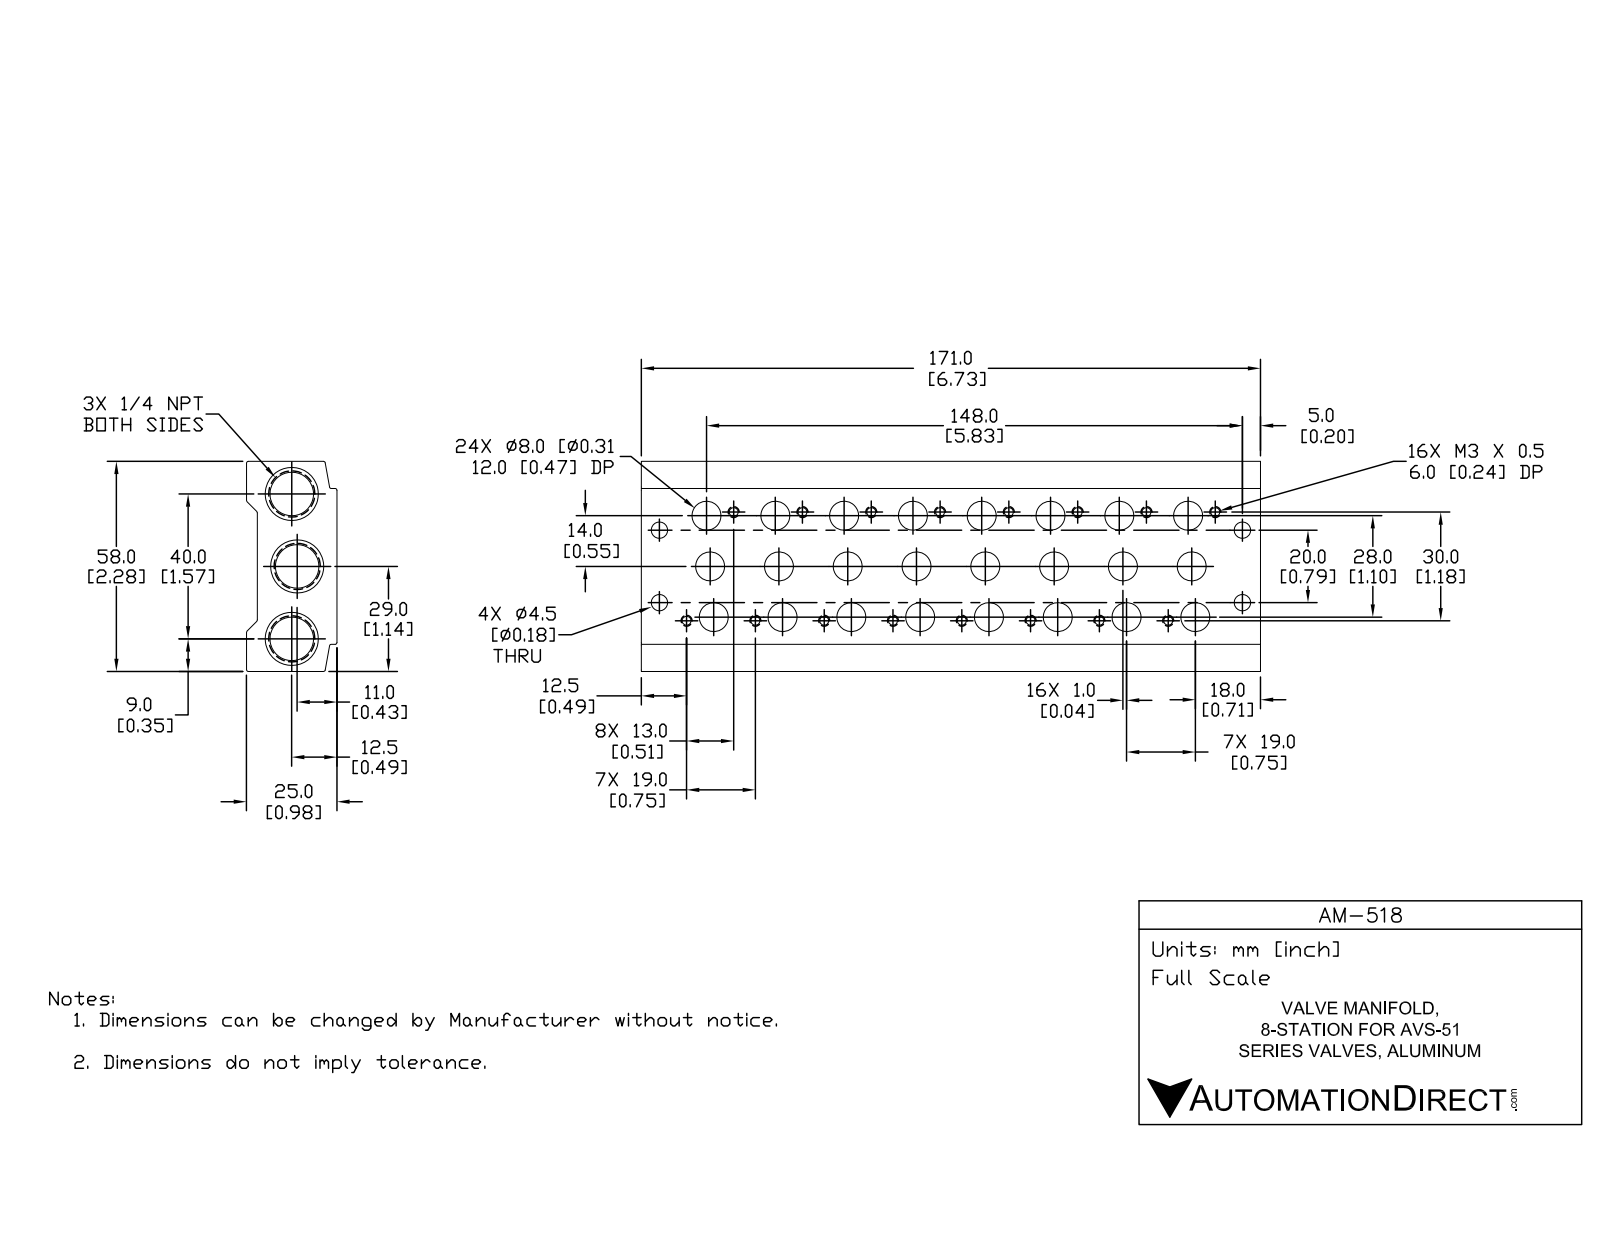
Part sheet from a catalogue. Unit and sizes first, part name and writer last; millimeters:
Units: millimetres
Overall size (bounding box): 171 × 58 × 25
Round holes (diameter × count): ⌀2.5 ×16, ⌀6.5 ×16, ⌀10.2 ×8, ⌀4.5 ×4, ⌀11.13 ×3
Partial cylindrical surfaces — rounded edges, fillets, slot ends (radius × count): R0.5 ×11
Main face-to-face distances: 22, 58, 3, 25, 171, 15, 12, 10, 6, 52
Hole centre spacings: 19, 38, 7.57, 29.52, 57, 76, 95, 11.54
Volume: 161 290 mm³ · Surface area: 53 397 mm²
Bodies: 1 solid, 185 faces (36 planar, 105 cylindrical, 44 other)
Part name (STEP PRODUCT): AM-518
STEP written by: SolidWorks 2015 (CONFIG_CONTROL_DESIGN)
